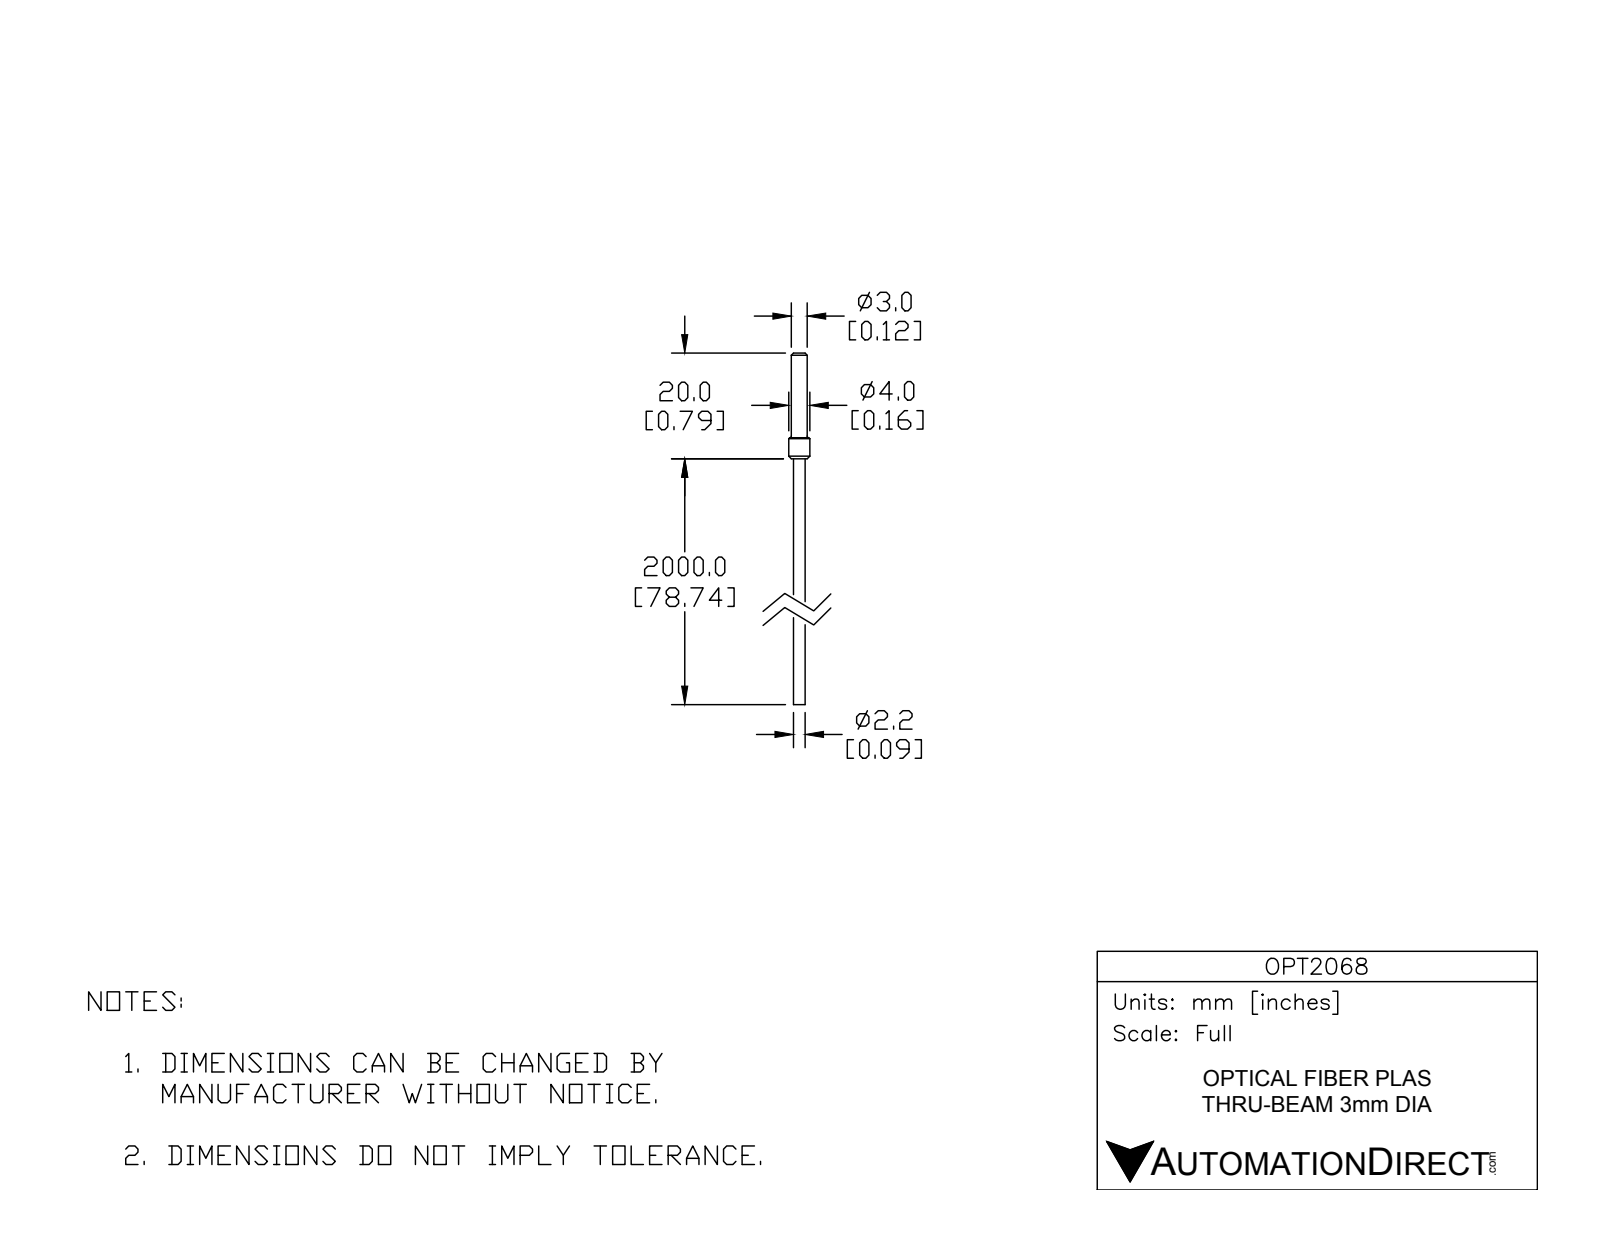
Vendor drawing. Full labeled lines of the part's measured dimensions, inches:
Part name (STEP PRODUCT): OPT2068
STEP written by: SolidWorks 2014 (AUTOMOTIVE_DESIGN)
Units: inches
Bodies: 1 solid, 17 faces (3 planar, 6 cylindrical, 8 other)
Overall size (bounding box): 2.618 × 0.157 × 0.157
Volume: 0.021 in³ · Surface area: 0.835 in²
Round bosses / shafts (diameter × count): ⌀0.157 ×1, ⌀0.118 ×1, ⌀0.087 ×1
Main face-to-face distances: 2.618, 1.831, 0.787
